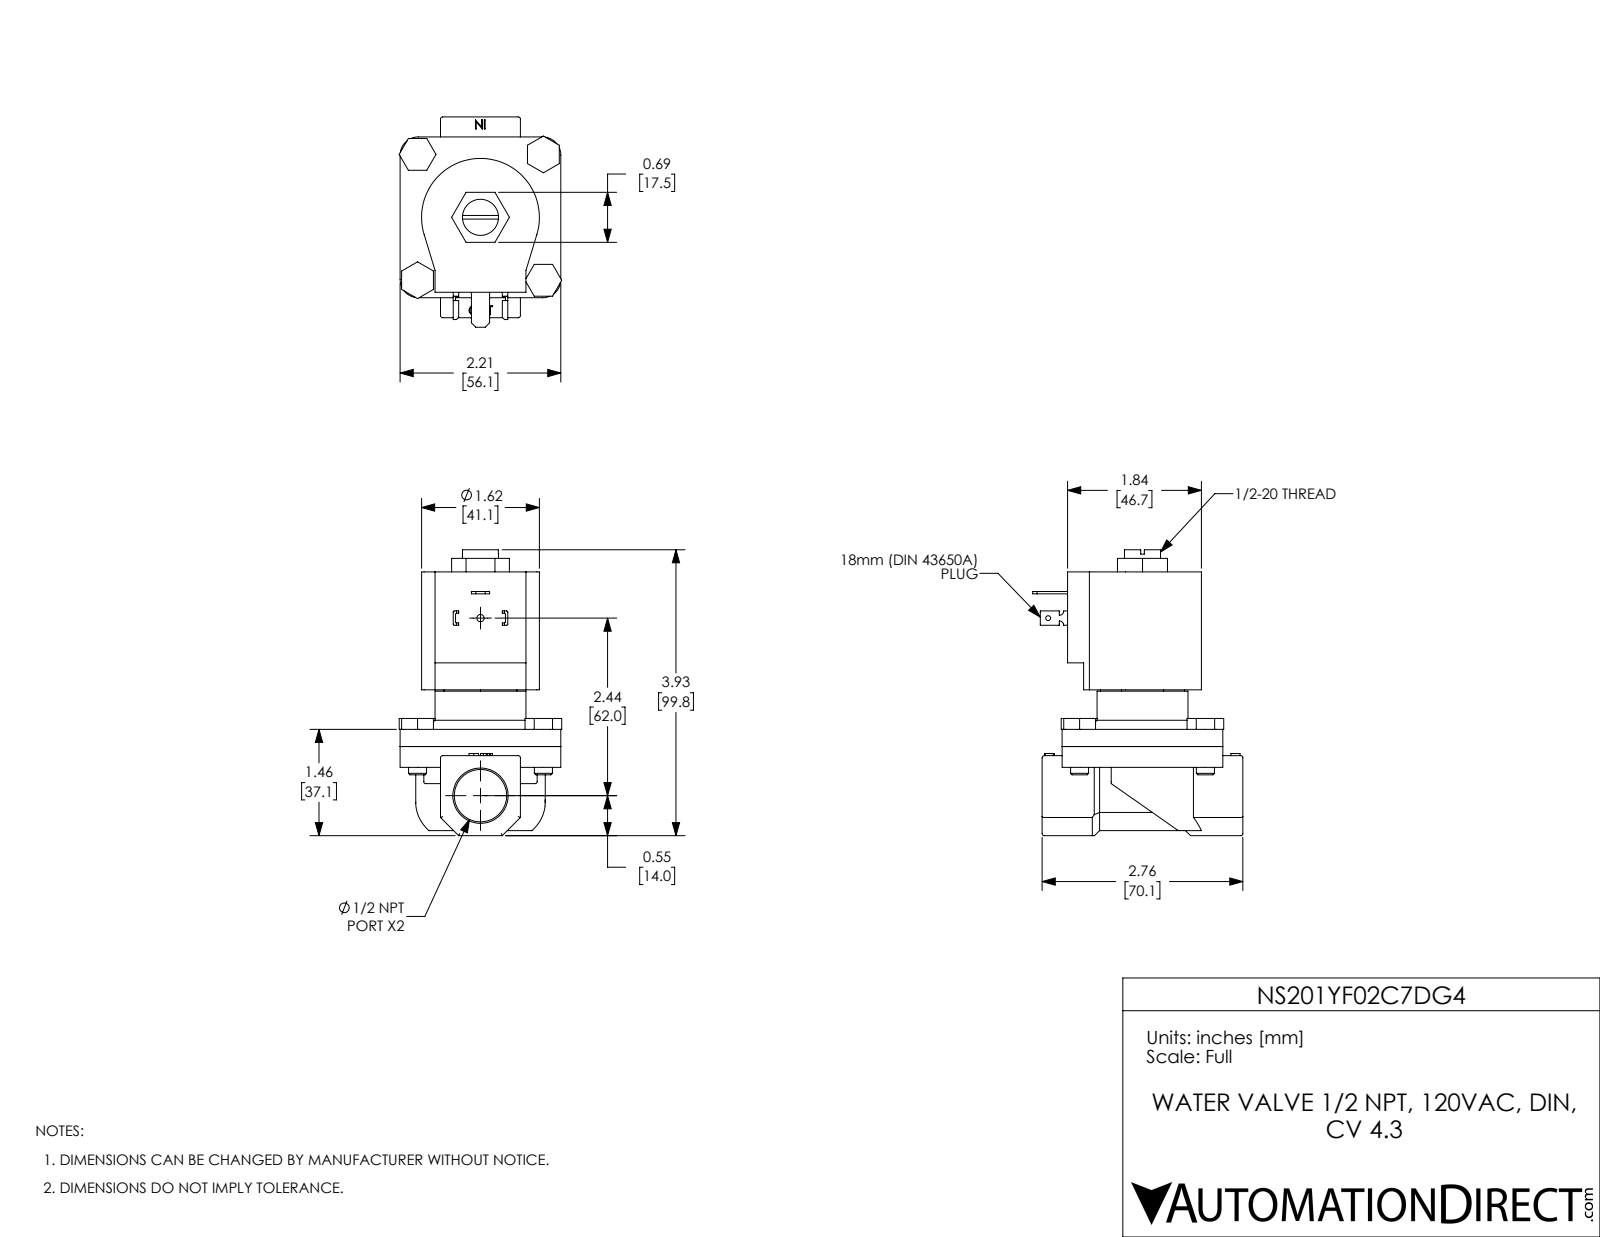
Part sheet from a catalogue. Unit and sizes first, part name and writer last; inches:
Units: inches
Overall size (bounding box): 3.93 × 2.89 × 2.235
Round holes (diameter × count): ⌀0.25 ×4, ⌀0.067 ×1, ⌀0.1 ×1, ⌀0.496 ×1, ⌀0.512 ×1, ⌀0.72 ×1, ⌀1.155 ×1
Round bosses / shafts (diameter × count): ⌀0.248 ×4, ⌀1.25 ×1
Partial cylindrical surfaces — rounded edges, fillets, slot ends (radius × count): R0.03 ×15, R0.015 ×8, R0.25 ×4, R0.06 ×2, R0.81 ×1, R0.89 ×1
Main face-to-face distances: 0.237, 0.237, 2.4, 2.4, 2.163, 0.556, 1.654, 0.286, 0.286, 0.523
Hole centre spacings: 1.223, 1.73, 2.446, 2.44
Volume: 9.82 in³ · Surface area: 63.44 in²
Bodies: 11 solids, 330 faces (196 planar, 99 cylindrical, 35 other)
Part name (STEP PRODUCT): NS201YF02C7DG4
STEP written by: SolidWorks 2021 (CONFIG_CONTROL_DESIGN)
